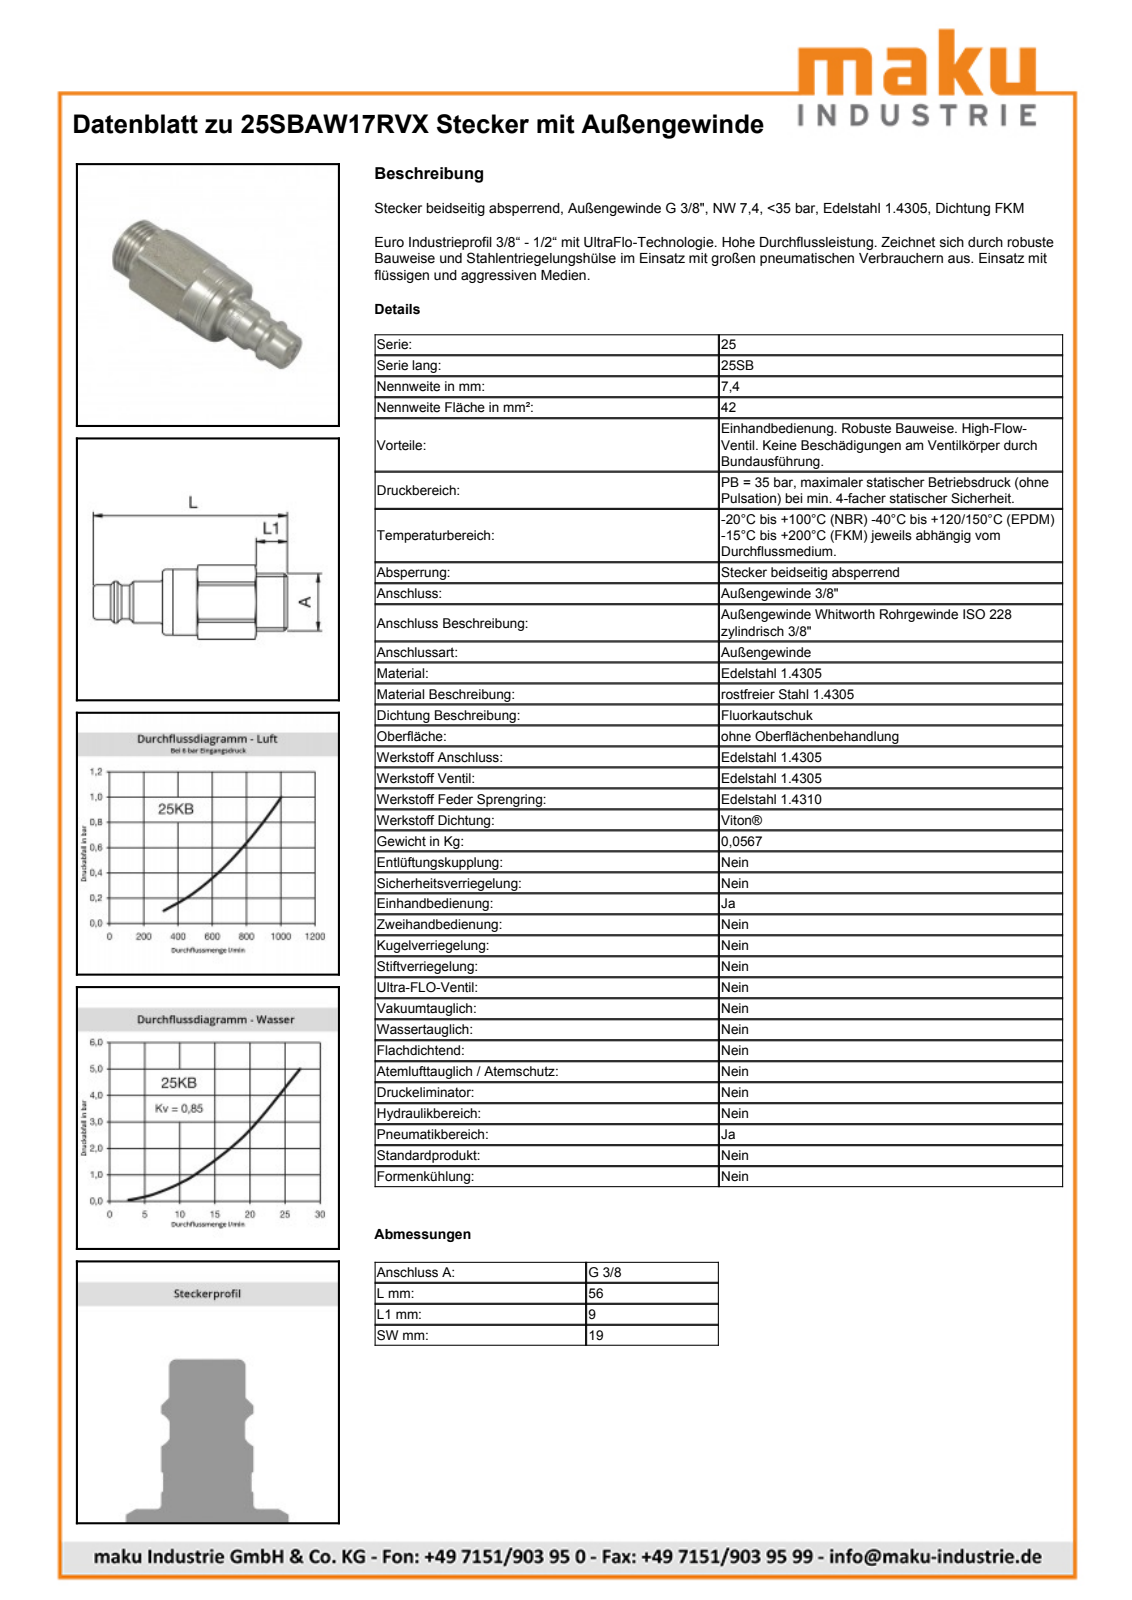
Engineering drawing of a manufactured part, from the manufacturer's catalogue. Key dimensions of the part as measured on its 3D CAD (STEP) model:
Part name (STEP PRODUCT): D106323
STEP written by: Autodesk Inventor 2011 (AUTOMOTIVE_DESIGN)
Units: millimetres
Bodies: 1 solid, 52 faces (14 planar, 17 cylindrical, 21 other)
Overall size (bounding box): 56 × 21.4 × 19.42
Volume: 11 809 mm³ · Surface area: 3 941 mm²
Round holes (diameter × count): ⌀16 ×1
Round bosses / shafts (diameter × count): ⌀19 ×1, ⌀18.95 ×1, ⌀16.66 ×1, ⌀15.3 ×1, ⌀12 ×1, ⌀9.9 ×1, ⌀9.75 ×1
Partial cylindrical surfaces — rounded edges, fillets, slot ends (radius × count): R10.7 ×1
Main face-to-face distances: 19, 19.02, 36, 20, 56, 47, 27, 9, 3, 4.5
